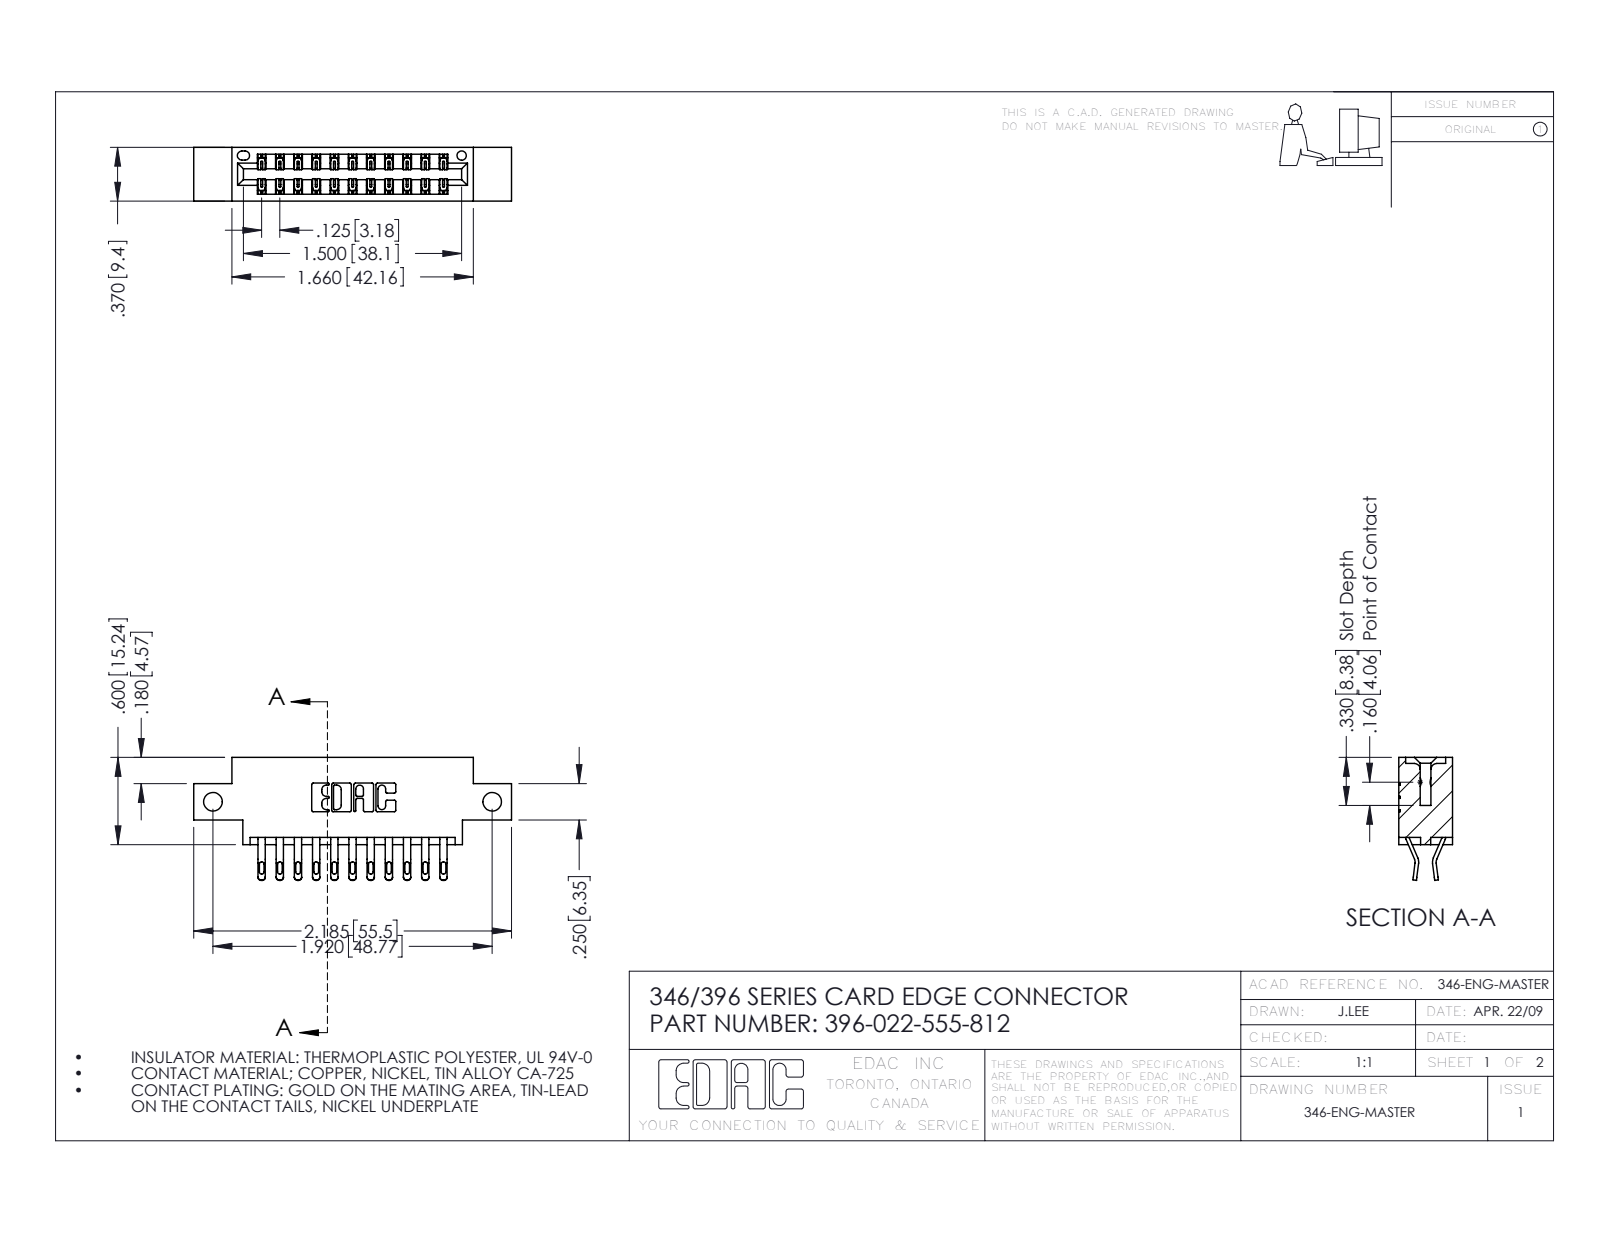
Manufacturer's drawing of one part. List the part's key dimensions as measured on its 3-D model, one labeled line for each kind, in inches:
Part name (STEP PRODUCT): 396-022-555-812; 345-292-001_555 Tail; 346 Part_0.170 Offset - Side Mount
STEP written by: SolidWorks 2016 (CONFIG_CONTROL_DESIGN)
Units: inches
Bodies: 23 solids, 1402 faces (806 planar, 596 cylindrical, 0 other)
Overall size (bounding box): 2.185 × 0.845 × 0.37
Volume: 0.305 in³ · Surface area: 10.3 in²
Round holes (diameter × count): ⌀0.128 ×2, ⌀0.064 ×1
Partial cylindrical surfaces — rounded edges, fillets, slot ends (radius × count): R0.016 ×44, R0.02 ×44, R0.006 ×33, R0.01 ×22, R0.007 ×6, R0.031 ×6, R0.026 ×3, R0.01 ×2
Main face-to-face distances: 0.25, 0.37, 0.048, 0.322, 0.025, 0.072, 0.298, 0.275, 0.148, 0.222
Hole centre spacings: 1.92
